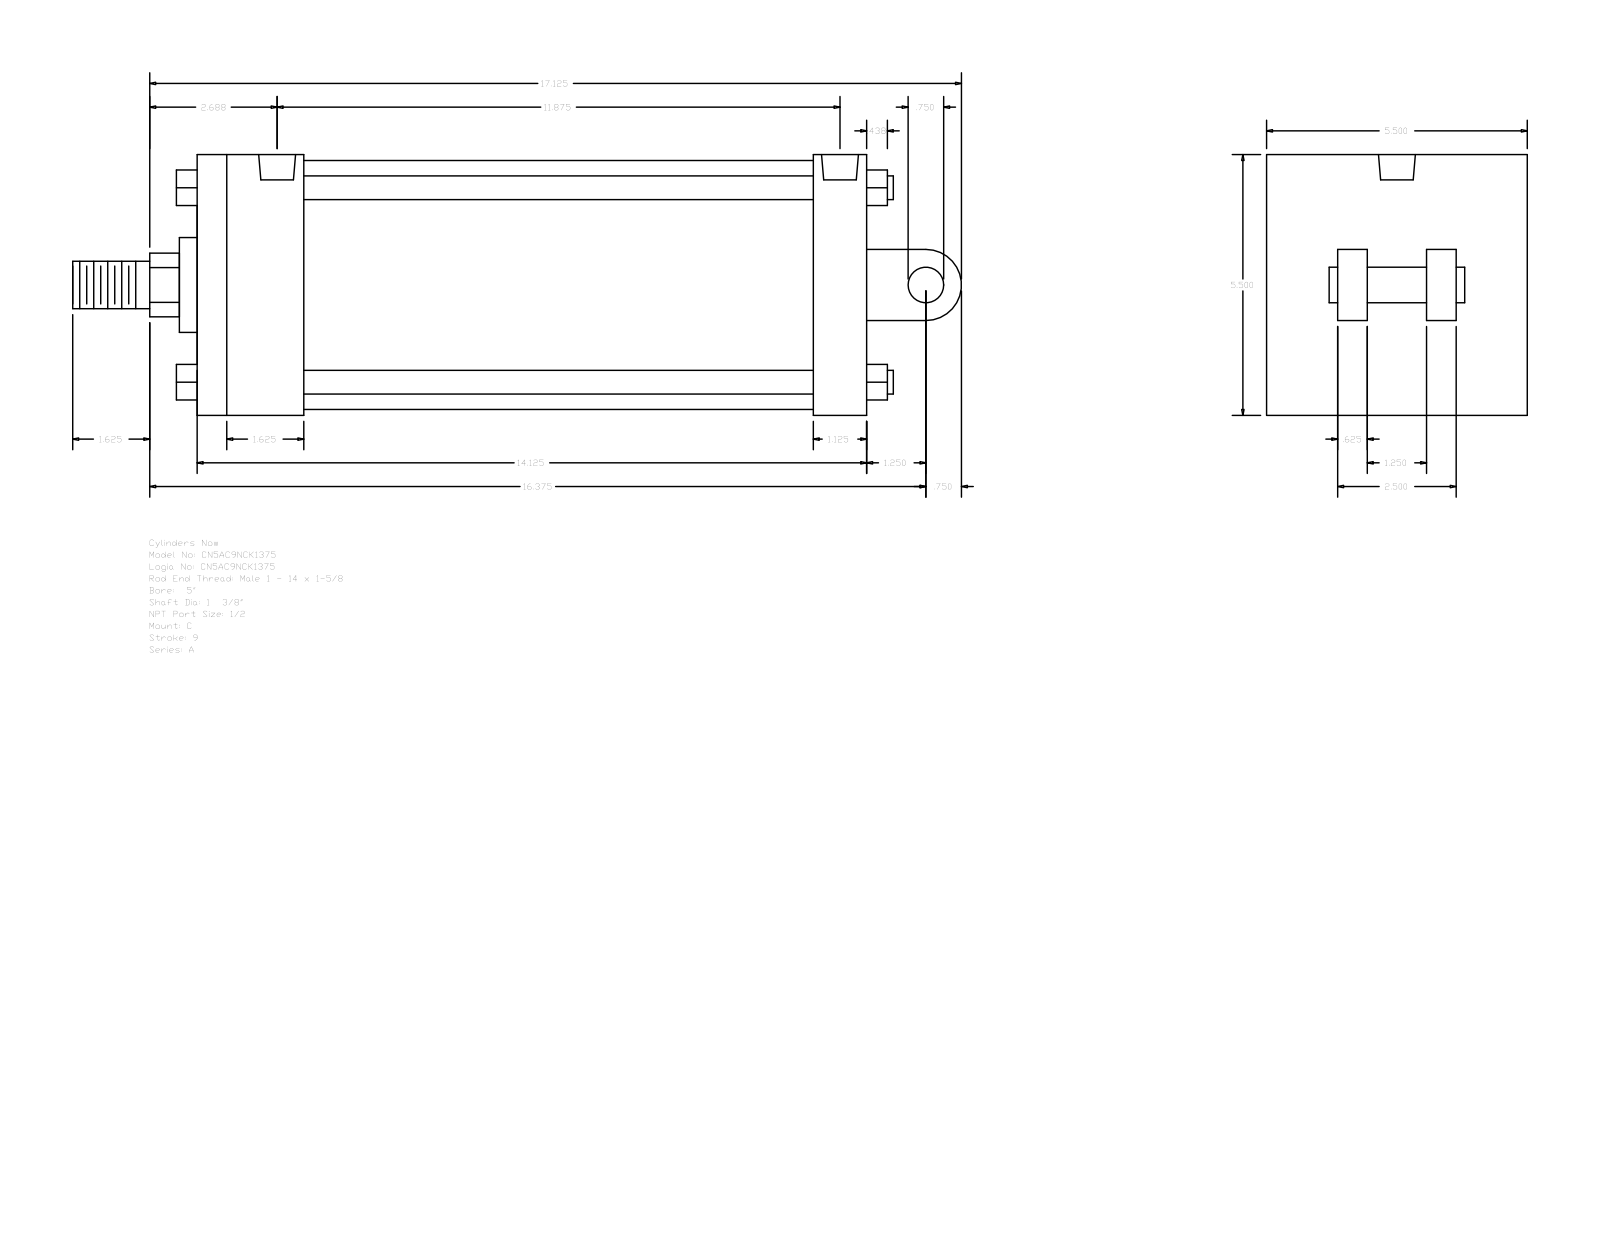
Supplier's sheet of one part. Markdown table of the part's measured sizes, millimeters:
| quantity | value |
| --- | --- |
| part name | A_C__0500_1.375 |
| STEP written by | GSSL Pune (CONFIG_CONTROL_DESIGN) |
| units | millimeters |
| bodies | 0 solids, 135 faces (102 planar, 33 cylindrical, 0 other) |
| overall size | 476.25 × 139.7 × 139.7 |
| round holes (diameter × count) | 8.73 × 4, 19.77 × 2 |
| round bosses / shafts (diameter × count) | 12.7 × 4, 133.35 × 1, 50.8 × 1, 34.92 × 1, 25.4 × 1, 19.05 × 1 |
| partial cylindrical surfaces (radius × count) | 17.06 × 1, 19.05 × 1 |
| main face-to-face distances | 139.7, 358.78, 57.15, 28.58, 330.2, 273.05, 301.63, 38.1, 53.97, 101.6 |
| hole center spacings | 2.39, 296.85, 299.24, 301.63 |
